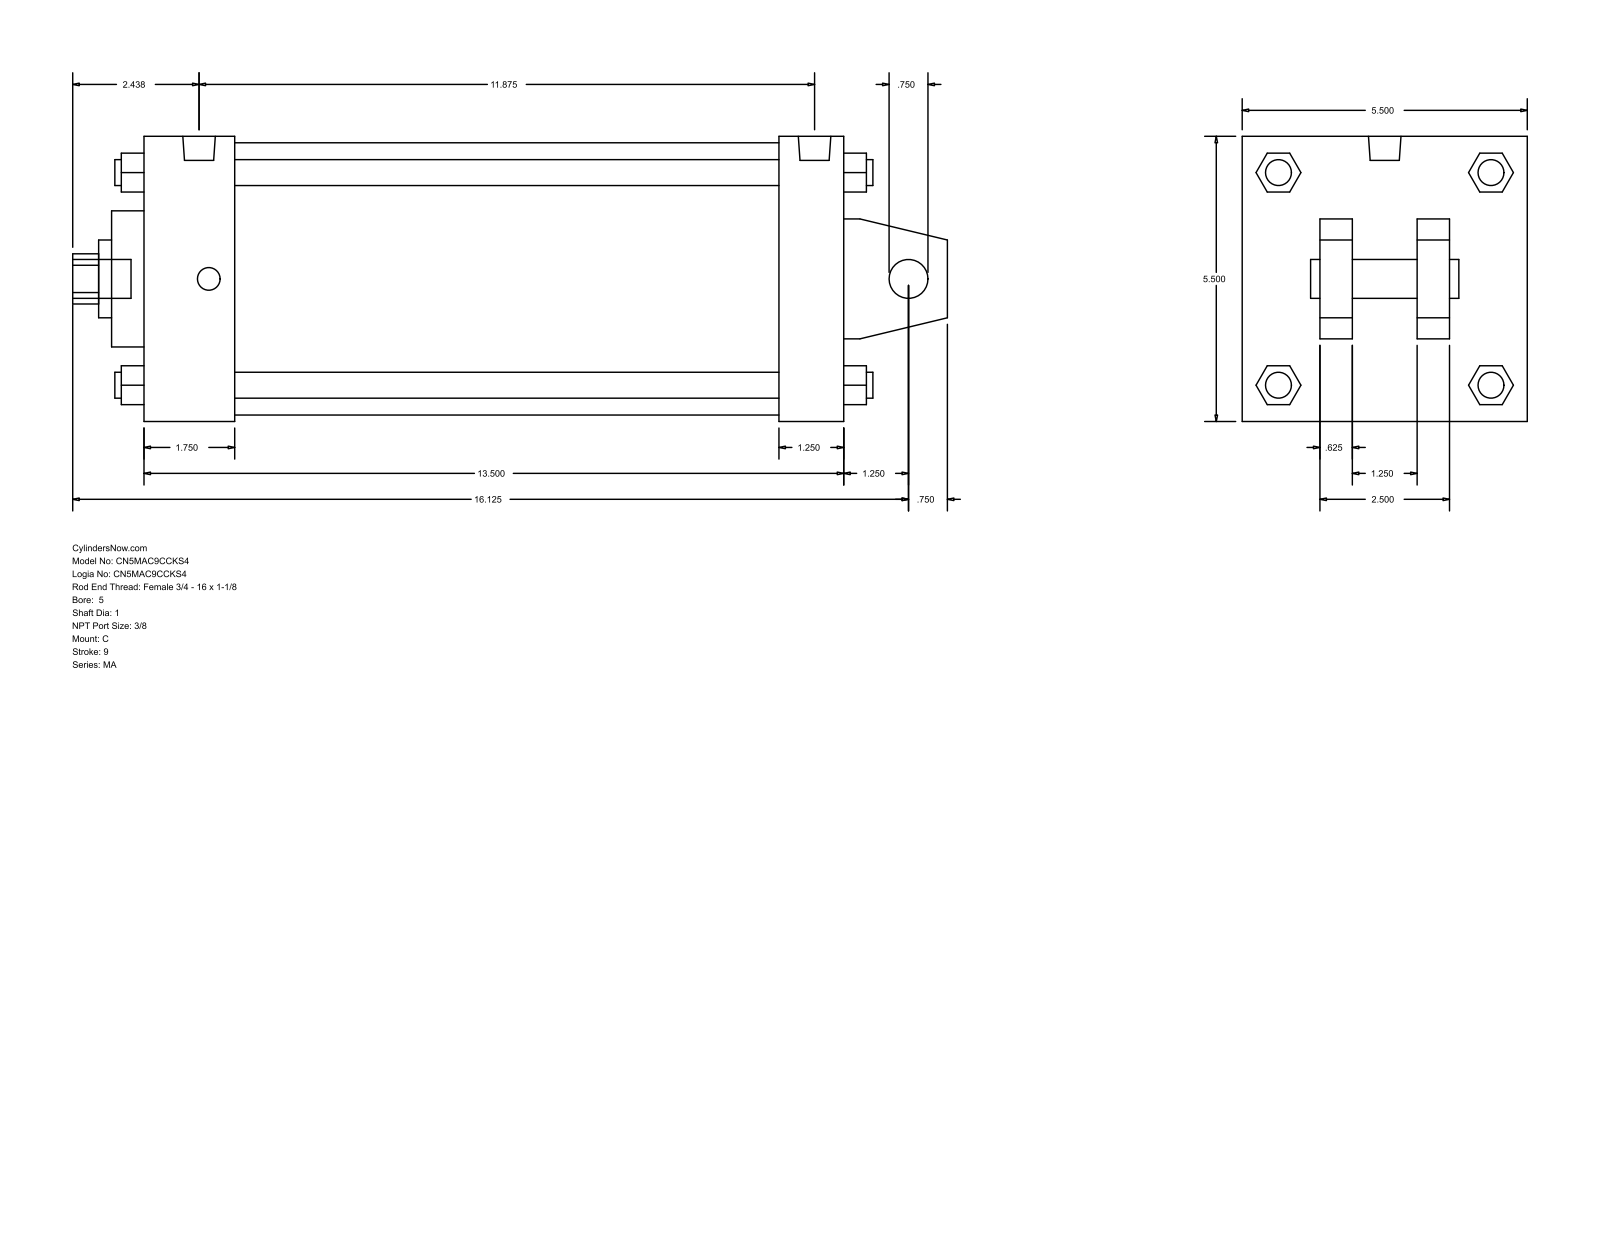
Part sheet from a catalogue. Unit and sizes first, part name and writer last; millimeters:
Units: millimetres
Overall size (bounding box): 428.62 × 139.7 × 139.7
Round holes (diameter × count): ⌀19.05 ×1, ⌀25.4 ×1, ⌀38.1 ×1, ⌀66.67 ×1, ⌀133.35 ×1
Round bosses / shafts (diameter × count): ⌀12.7 ×4, ⌀11.11 ×4, ⌀15.93 ×2, ⌀19.05 ×1
Partial cylindrical surfaces — rounded edges, fillets, slot ends (radius × count): R12.29 ×1
Main face-to-face distances: 139.7, 342.9, 15.87, 311.15, 31.75, 44.46, 266.69, 298.44, 38.1, 101.6
Bodies: 0 solids, 141 faces (109 planar, 32 cylindrical, 0 other)
Part name (STEP PRODUCT): MA_C__0500_1
STEP written by: GSSL Pune (CONFIG_CONTROL_DESIGN)
